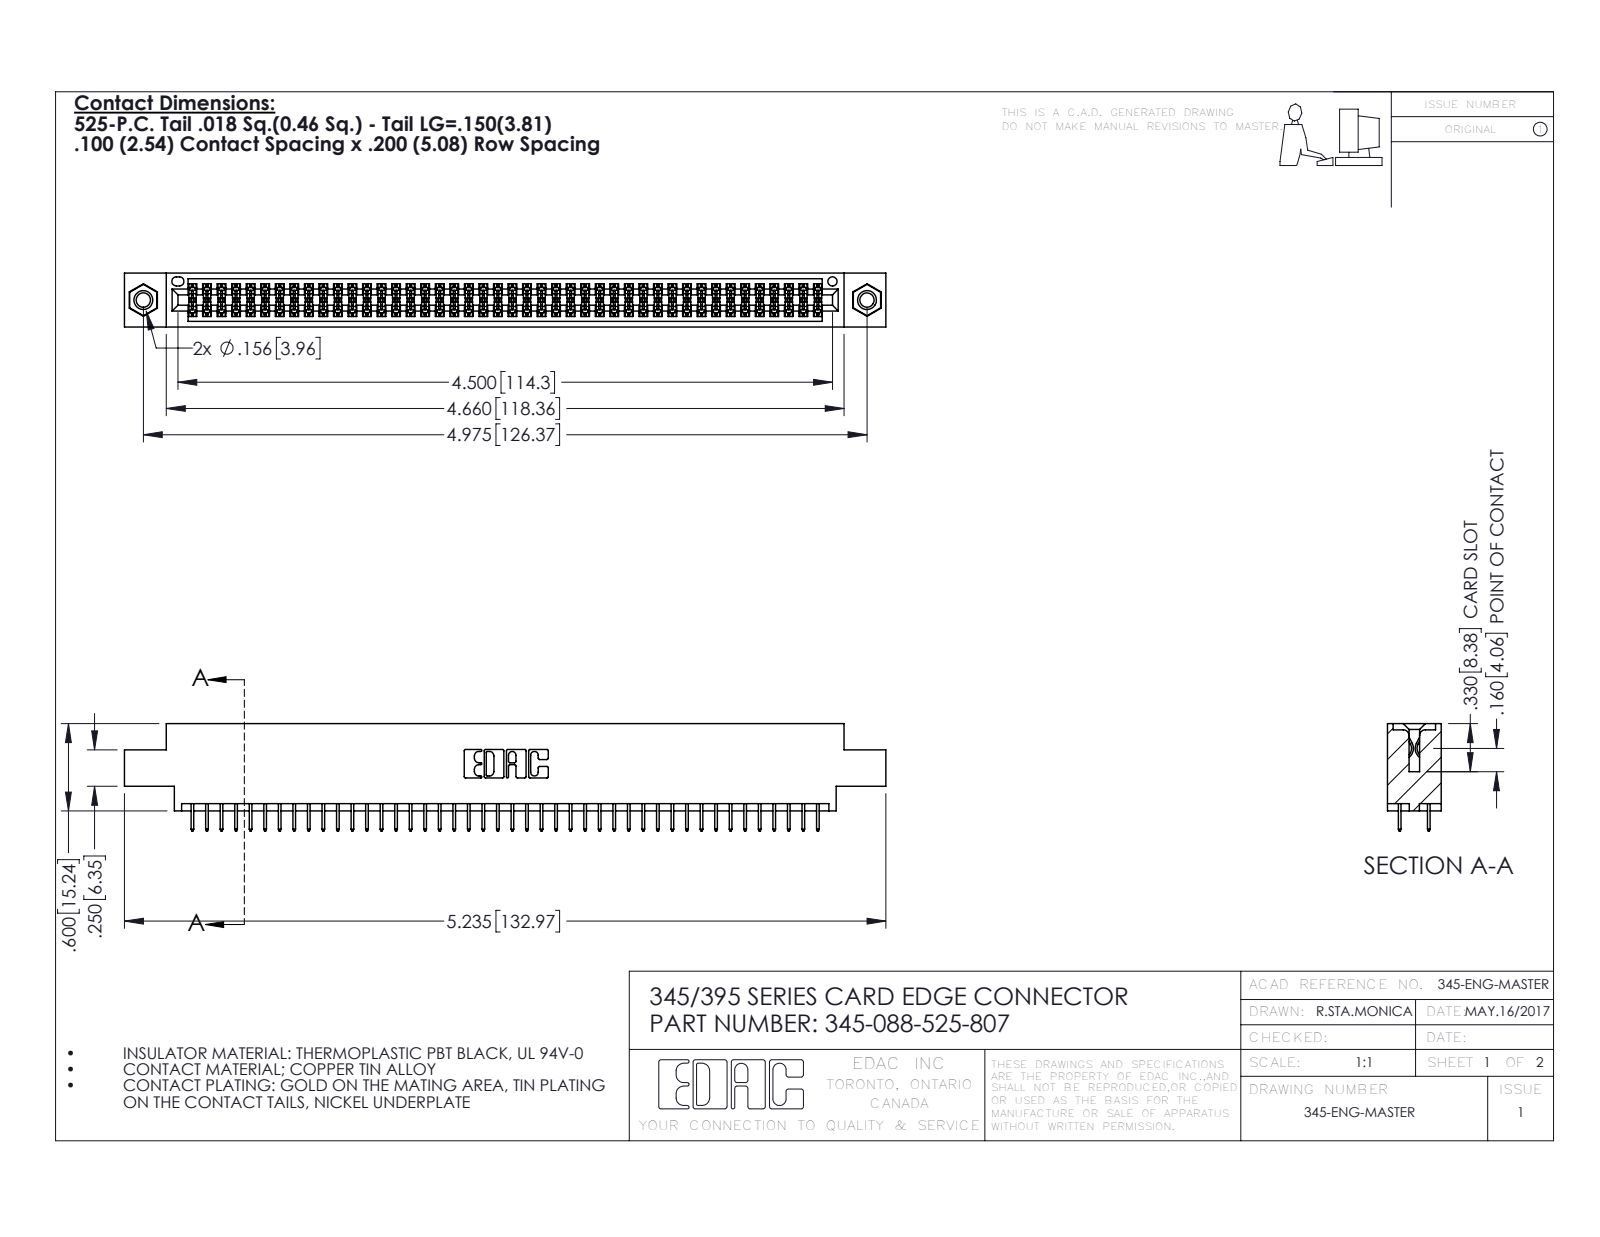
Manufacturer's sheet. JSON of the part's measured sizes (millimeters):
{"part_name": "345-088-525-807; 345-250-001_345-250-005-103; 345 Part_0.170 Offset - 0.156 Dia-TI; 345-292-001_345-293-125", "step_written_by": "SolidWorks 2020 (CONFIG_CONTROL_DESIGN)", "units": "millimeters", "bodies": {"solids": 91, "faces": 4942, "planar": 3548, "cylindrical": 1378, "other": 16}, "overall_size": [133, 18.7, 9.4], "volume_mm3": 12700, "surface_area_mm2": 18490, "round_holes": [[2.5, 2], [3.2, 2], [4, 2], [1.6, 1]], "round_bosses_or_shafts": [[3.9, 2]], "partial_cylinders_radius": [[0.2, 132], [0.3, 22], [0.2, 6], [0.8, 6], [0.7, 3], [0.4, 2], [0.5, 2], [0.6, 2]], "face_to_face_distances": [1.8, 7.6, 9.4, 5.1, 2.5, 6.9, 0.6, 5.7, 4.4, 1.8], "hole_center_spacings": [6.9, 120.4, 126.4]}
